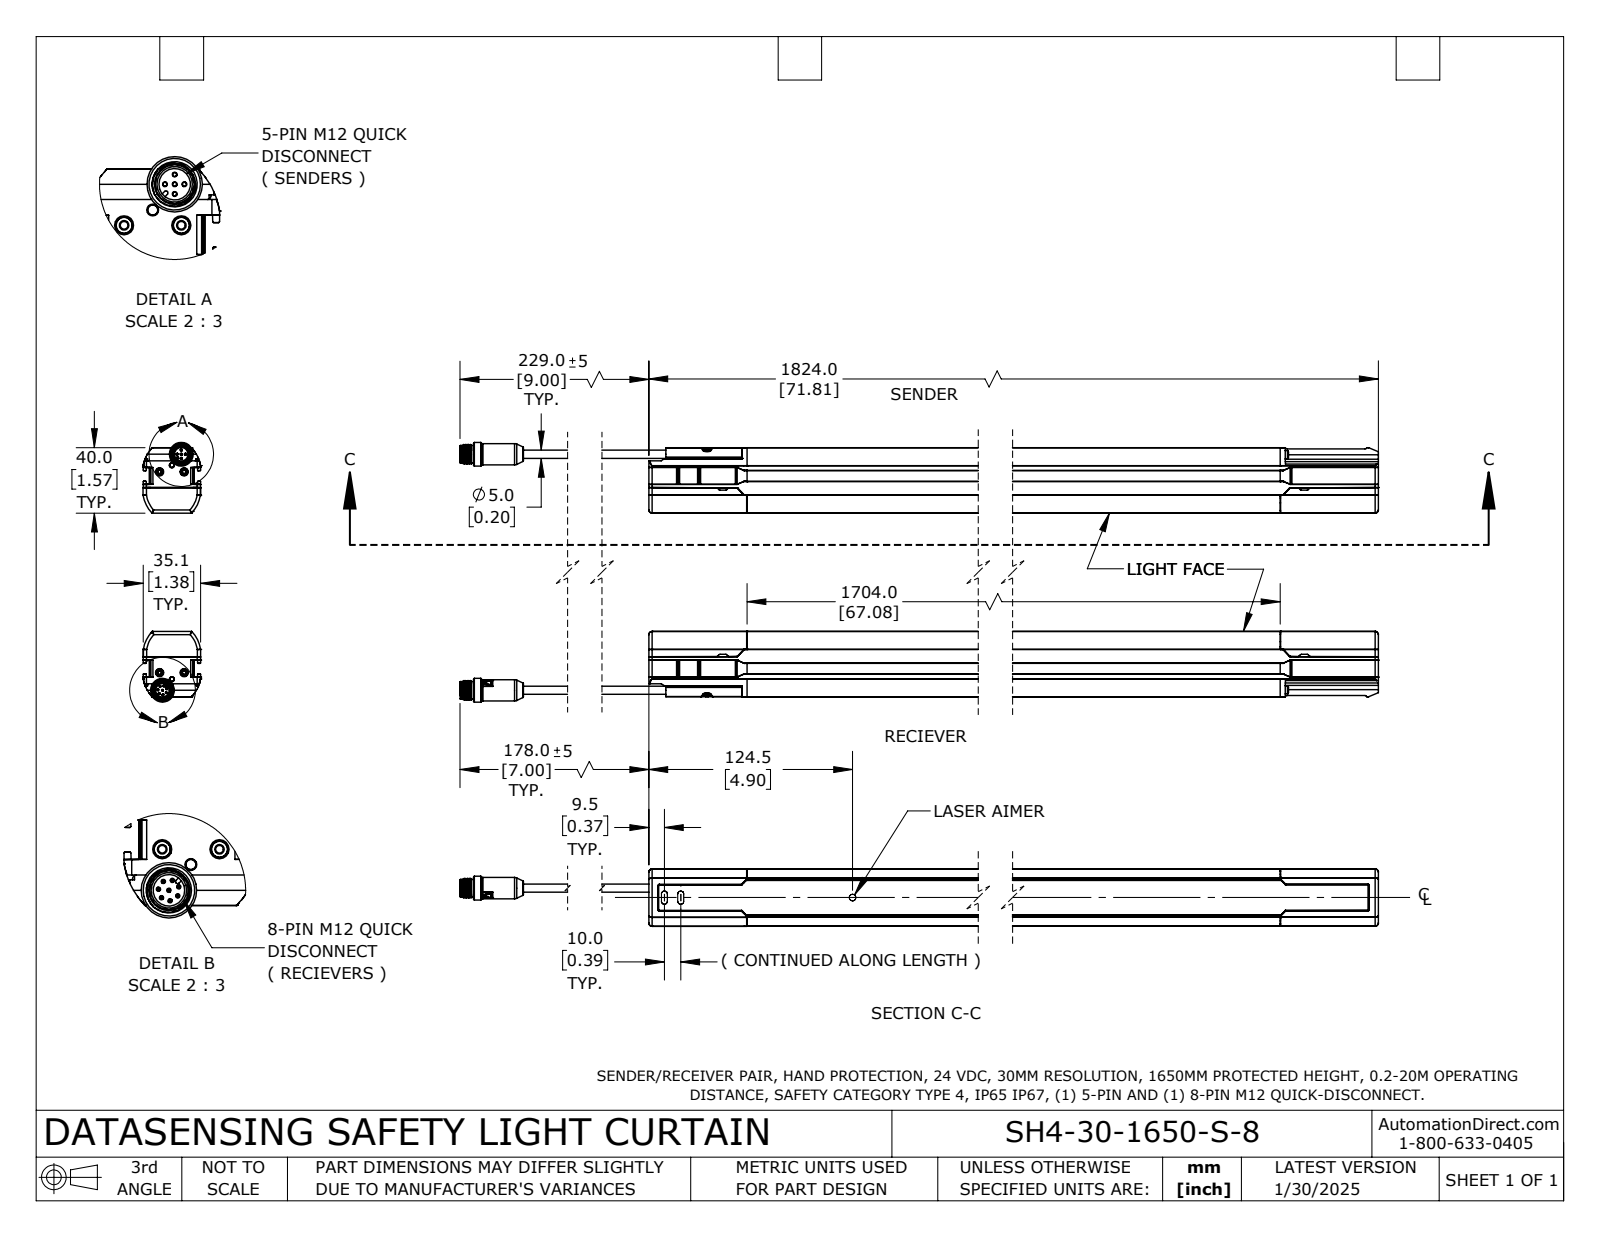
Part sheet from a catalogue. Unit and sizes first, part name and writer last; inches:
Units: inches
Overall size (bounding box): 74.303 × 6.248 × 1.384
Round holes (diameter × count): ⌀0.079 ×4, ⌀0.118 ×4, ⌀0.197 ×4, ⌀0.1 ×2, ⌀0.1 ×2, ⌀0.1 ×2, ⌀0.101 ×2, ⌀0.325 ×2, ⌀0.382 ×2, ⌀0.407 ×2, ⌀0.425 ×2, ⌀0.11 ×1
Round bosses / shafts (diameter × count): ⌀0.197 ×10, ⌀0.087 ×8, ⌀0.031 ×8, ⌀0.039 ×5, ⌀0.172 ×4, ⌀0.571 ×2, ⌀0.512 ×2, ⌀0.417 ×2
Partial cylindrical surfaces — rounded edges, fillets, slot ends (radius × count): R0.01 ×164, R0.016 ×66, R0.02 ×50, R0.008 ×36, R0.031 ×20, R0.031 ×12, R0.079 ×12, R0.059 ×10
Main face-to-face distances: 1.496, 4.496, 0.156, 1.222, 3, 5.992, 1.378, 1.067, 4.634, 0.069
Hole centre spacings: 0.866, 5.11, 5.183, 0.429, 0.591, 0.672, 4.831, 4.867
Volume: 239.8 in³ · Surface area: 999.5 in²
Bodies: 4 solids, 2608 faces (1186 planar, 784 cylindrical, 638 other)
Part name (STEP PRODUCT): SH4-30-1650-S-8
STEP written by: SolidWorks 2024 (AUTOMOTIVE_DESIGN)
